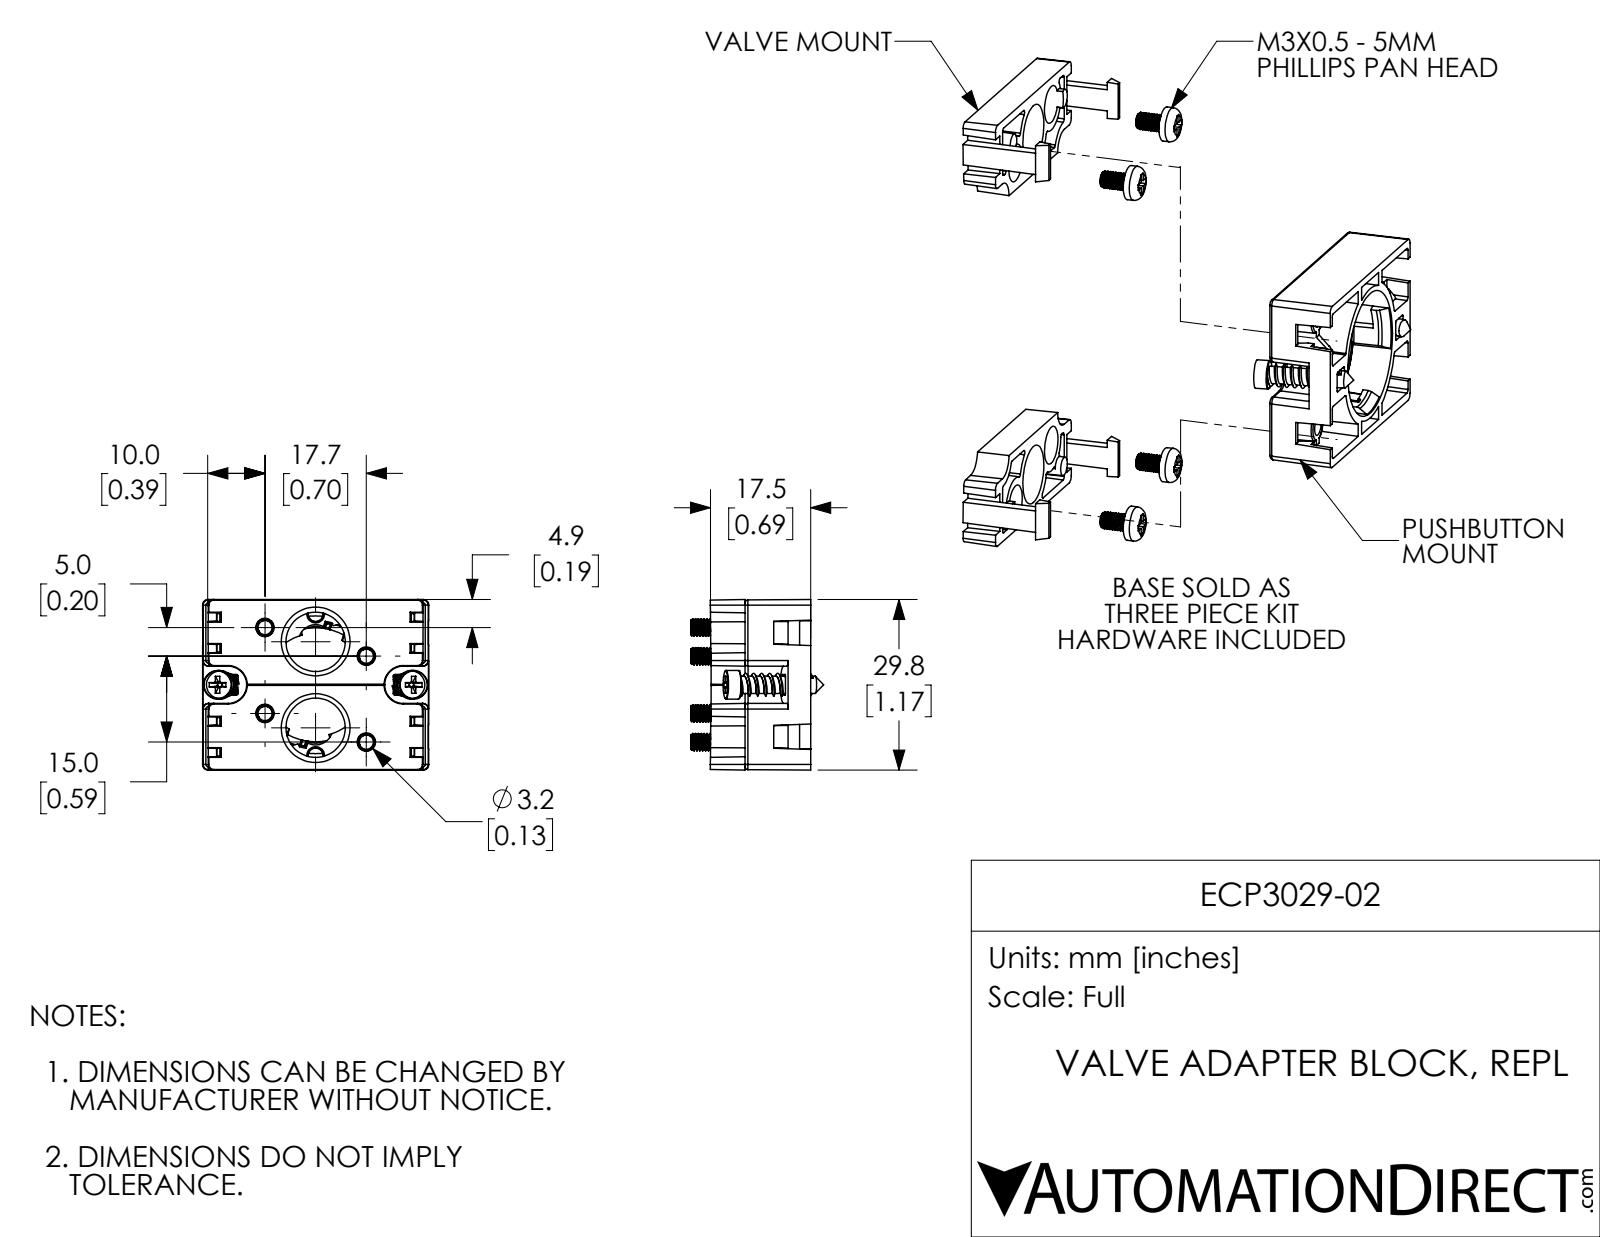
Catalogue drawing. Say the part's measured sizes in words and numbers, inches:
The part is named "ECP3029-02". Its 3-D file was written by "SolidWorks 2017 (AUTOMOTIVE_DESIGN)". It is 2 solids with 194 faces: 98 planar, 4 cylindrical and 92 other. Overall it measures 1.483 by 1.173 by 0.613 inches. Its volume is 0.239 cubic inches and its surface area 7.868 square inches. Round holes: 2 of diameter 0.407. The main face-to-face distances are 0.587, 0.177, 0.715, 0.059, 0.366, 0.528, 0.053, 0.052, 0.138, 0.656. The hole center spacings are 0.591.
